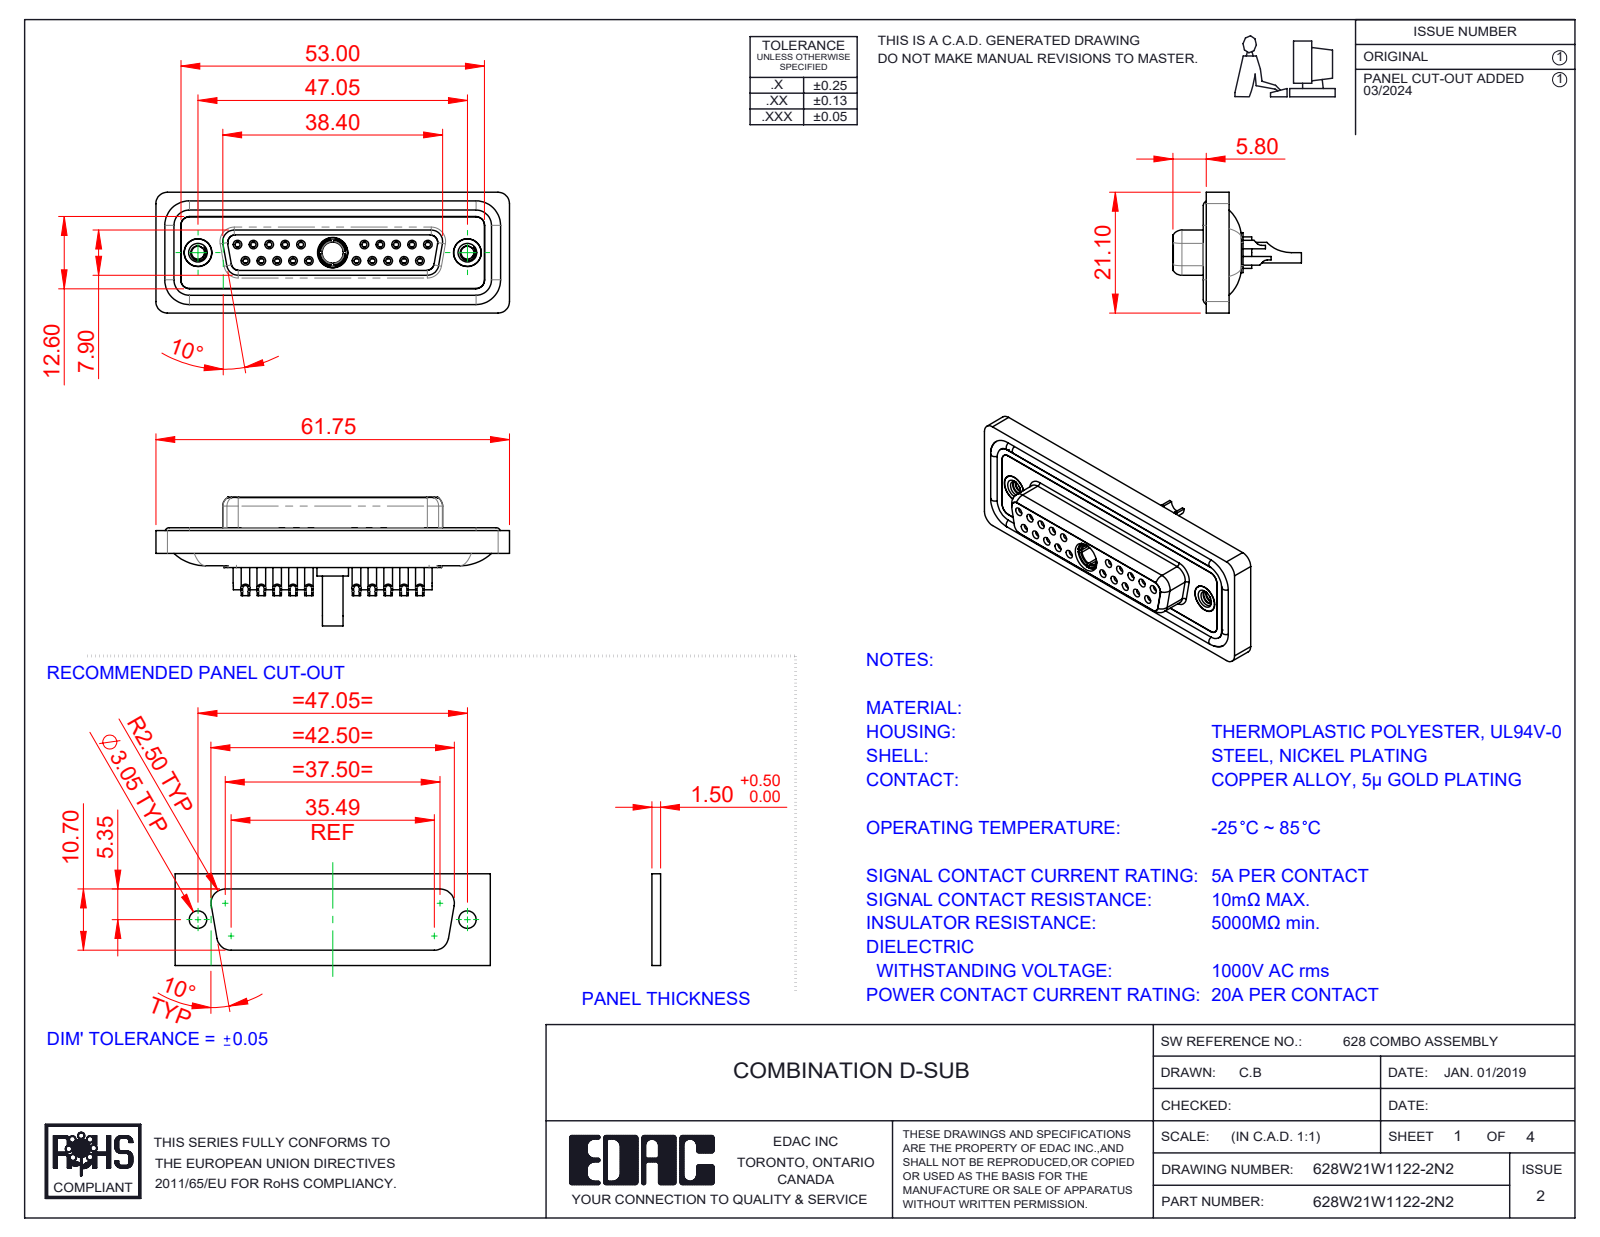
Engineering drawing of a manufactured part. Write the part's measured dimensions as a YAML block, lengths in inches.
part_name: "628Combo Waterproof Housing_25 Contacts; Power Socket_20A SC; 628W21W1122-2N2; 628Combo Threaded Rivet_2 (+5 more)"
step_written_by: "SolidWorks 2023 (CONFIG_CONTROL_DESIGN)"
units: inches
bodies: {solids: 29, faces: 1566, planar: 477, cylindrical: 634, other: 455}
overall_size: [2.431, 0.884, 0.831]
volume: 0.514
surface_area: 22.16
round_holes:
  - {diameter: 0.035, count: 20}
  - {diameter: 0.039, count: 20}
  - {diameter: 0.043, count: 20}
  - {diameter: 0.059, count: 20}
  - {diameter: 0.079, count: 20}
  - {diameter: 0.063, count: 10}
  - {diameter: 0.067, count: 10}
  - {diameter: 0.191, count: 3}
  - {diameter: 0.089, count: 2}
  - {diameter: 0.157, count: 2}
  - {diameter: 0.159, count: 2}
  - {diameter: 0.197, count: 2}
round_bosses_or_shafts:
  - {diameter: 0.087, count: 20}
  - {diameter: 0.063, count: 14}
  - {diameter: 0.195, count: 2}
  - {diameter: 0.189, count: 2}
  - {diameter: 0.217, count: 1}
  - {diameter: 0.205, count: 1}
  - {diameter: 0.195, count: 1}
  - {diameter: 0.187, count: 1}
partial_cylinders:
  - {radius: 0.059, count: 22}
  - {radius: 0.079, count: 18}
  - {radius: 0.053, count: 8}
  - {radius: 0.063, count: 8}
  - {radius: 0.039, count: 6}
  - {radius: 0.01, count: 4}
  - {radius: 0.02, count: 4}
  - {radius: 0.024, count: 4}
face_to_face_distances: [0.016, 0.071, 0.293, 0.222, 0.26, 0.02, 0.063, 0.278, 0.114, 0.043]
hole_center_spacings: [0.124, 0.109, 0.218, 0.198, 0.327, 0.294, 0.654, 0.763]
